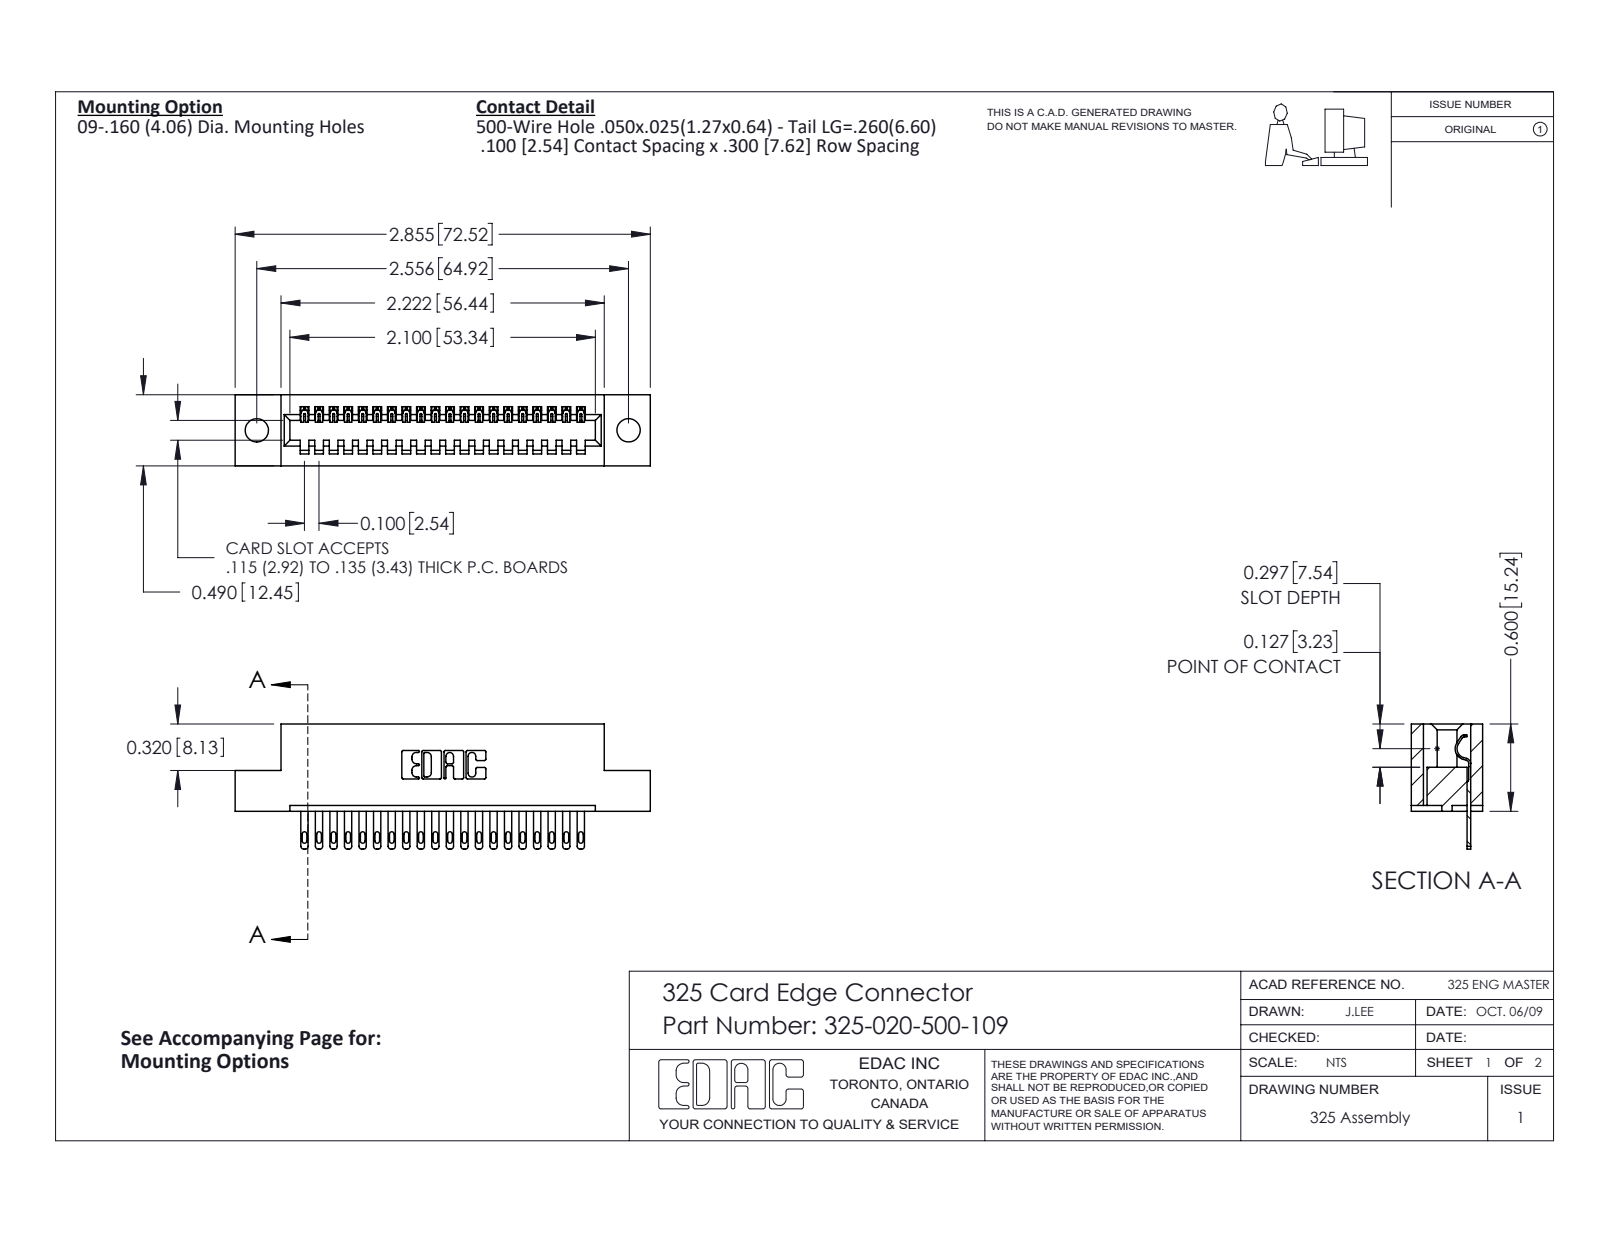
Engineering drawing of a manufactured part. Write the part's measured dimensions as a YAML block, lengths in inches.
part_name: "325-020-500-109; 325 Part_.160 TH; 325-292-001_325-293-100"
step_written_by: "SolidWorks 2016 (CONFIG_CONTROL_DESIGN)"
units: inches
bodies: {solids: 21, faces: 1194, planar: 790, cylindrical: 404, other: 0}
overall_size: [2.855, 0.86, 0.49]
volume: 0.538
surface_area: 14.26
round_holes:
  - {diameter: 0.16, count: 2}
partial_cylinders:
  - {radius: 0.006, count: 40}
  - {radius: 0.016, count: 40}
  - {radius: 0.02, count: 40}
  - {radius: 0.01, count: 22}
  - {radius: 0.007, count: 6}
  - {radius: 0.031, count: 6}
  - {radius: 0.026, count: 3}
  - {radius: 0.014, count: 1}
face_to_face_distances: [0.083, 0.407, 0.3, 0.49, 0.107, 0.383, 0.025, 0.04, 0.1, 0.325]
hole_center_spacings: [2.556]
